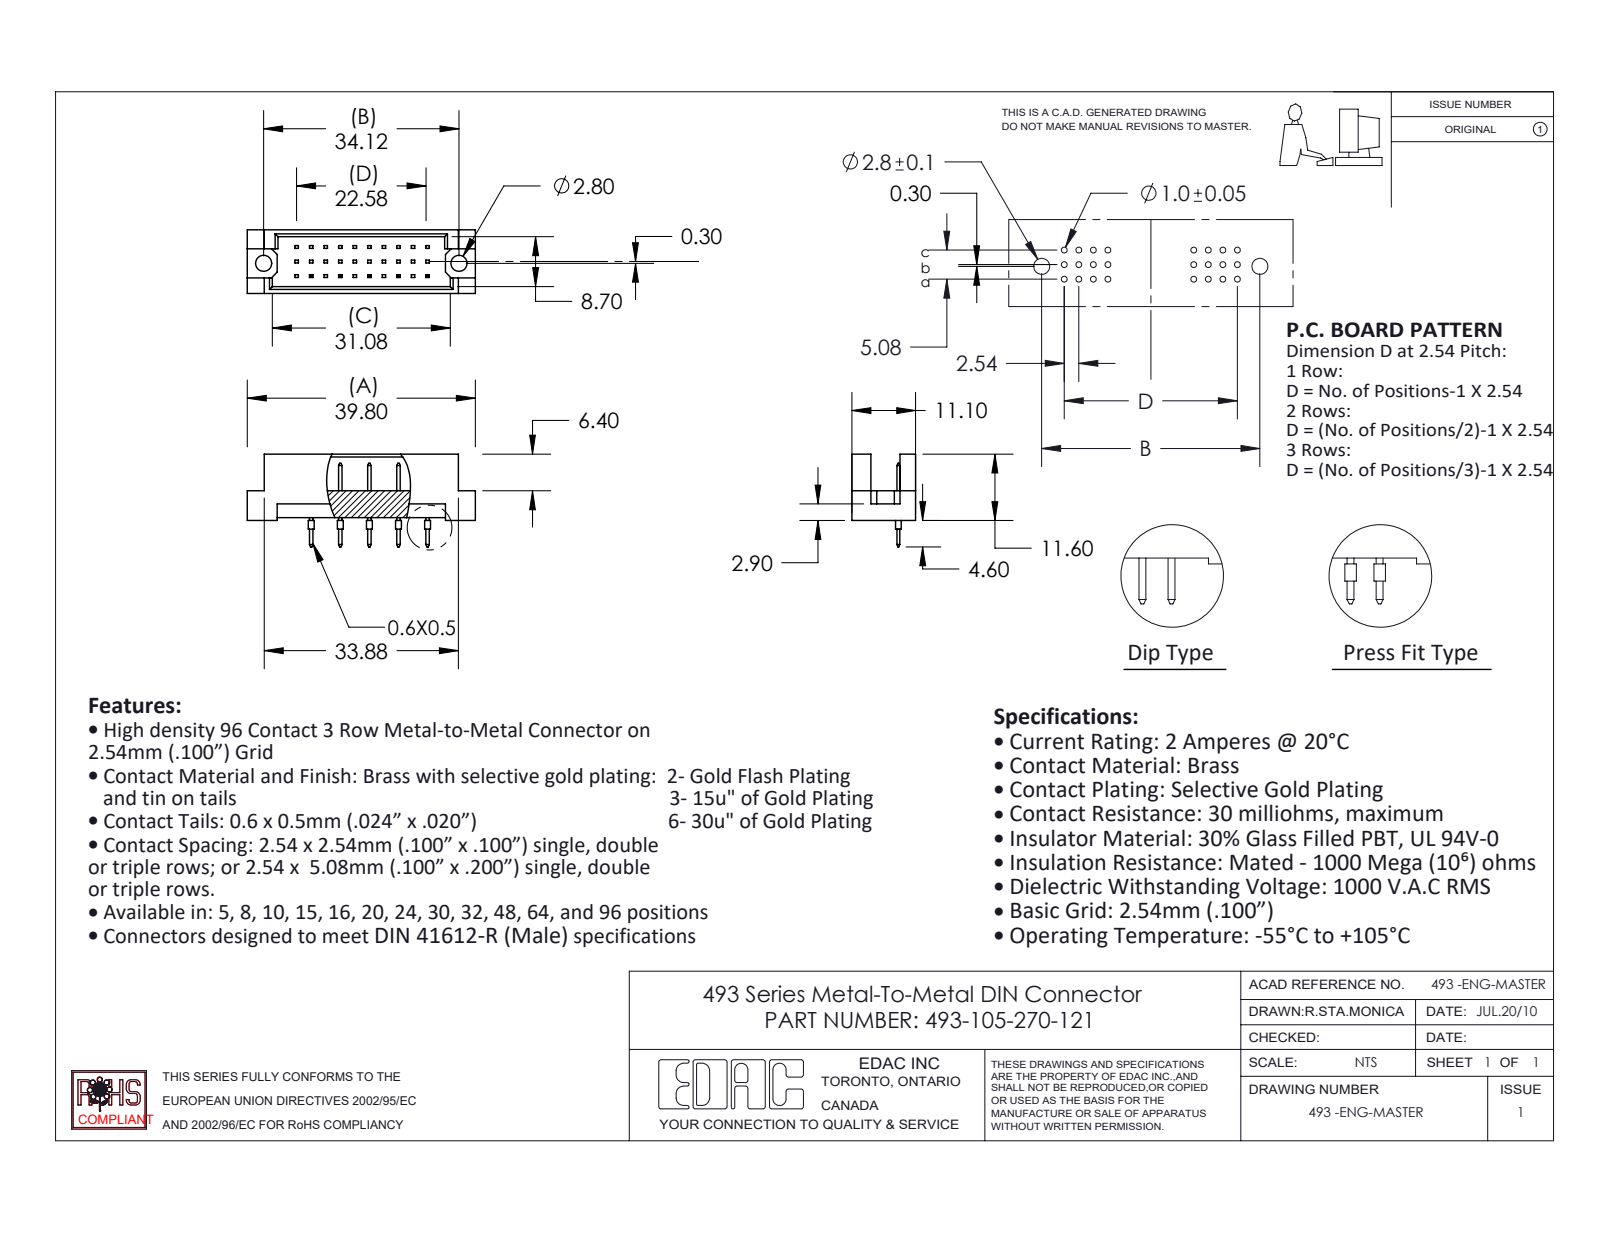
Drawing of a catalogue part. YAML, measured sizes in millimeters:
part_name: "493-290_70; 493-105-270-122; 493 Part_30"
step_written_by: "SolidWorks 2020 (CONFIG_CONTROL_DESIGN)"
units: millimeters
bodies: {solids: 6, faces: 282, planar: 268, cylindrical: 14, other: 0}
overall_size: [39.8, 16.2, 11.1]
volume: 2398
surface_area: 2908
round_holes:
  - {diameter: 2.8, count: 2}
round_bosses_or_shafts:
  - {diameter: 1, count: 5}
face_to_face_distances: [1.2, 9.9, 11.1, 8.7, 4.7, 0.5, 5.08, 2.4, 2.54, 2.3]
hole_center_spacings: [34.12]
